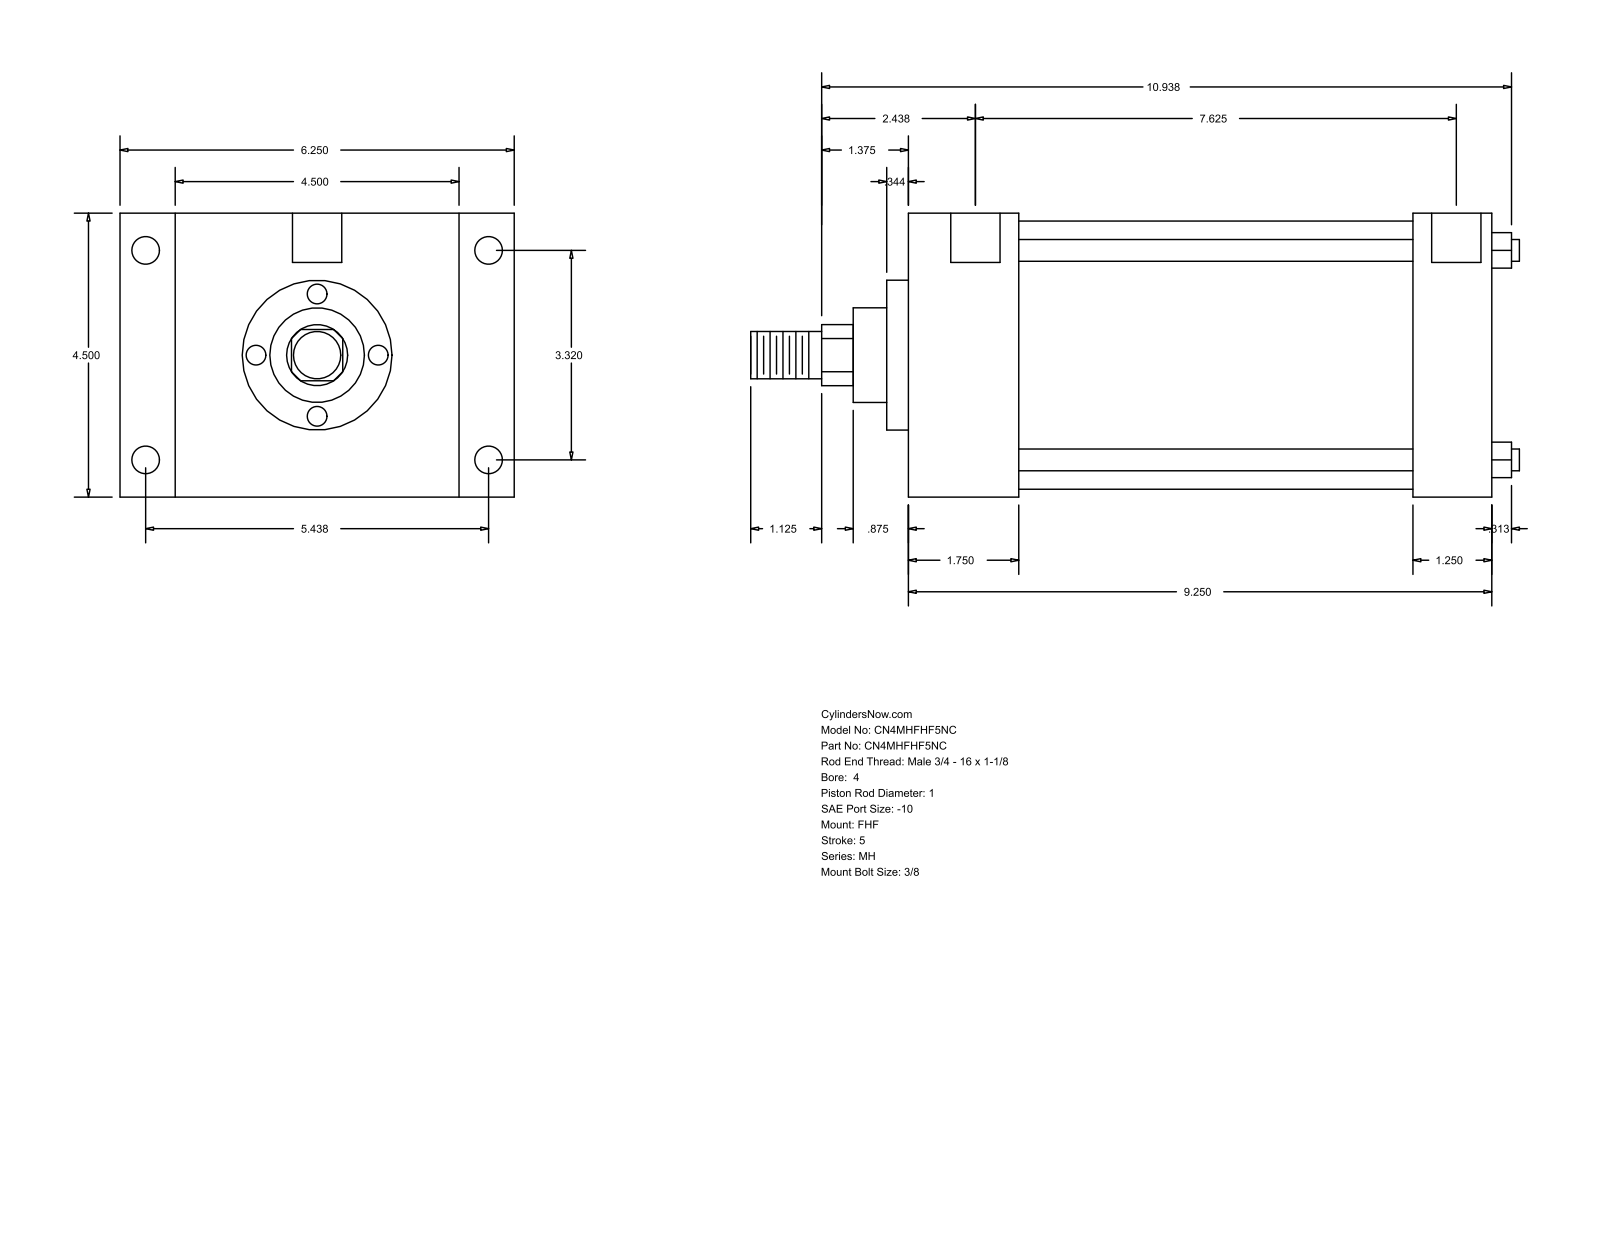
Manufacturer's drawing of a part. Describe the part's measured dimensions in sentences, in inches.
The part is named "MH_FHF__0400_1". Its 3-D file was written by "GSSL Pune (CONFIG_CONTROL_DESIGN)". It is 0 solids with 90 faces: 61 planar, 29 cylindrical and 0 other. Overall it measures 12.187 by 6.25 by 4.5 inches. Round holes: 4 of diameter 0.344, 4 of diameter 0.438, 2 of diameter 0.781. Round bosses or shafts: 4 of diameter 0.345, 1 of diameter 4.25, 1 of diameter 2.375, 1 of diameter 1.5, 1 of diameter 1, 1 of diameter 0.75. Partial cylindrical surfaces (rounded edges, fillets, slot ends): 1 of radius 0.484. The main face-to-face distances are 4.5, 9.25, 1.75, 7.5, 0.875, 5.375, 6.25, 6.25, 8, 1.25. The hole center spacings are 3.32, 5.438, 6.371, 7.75, 0.062, 0.063, 7.625, 7.687.
